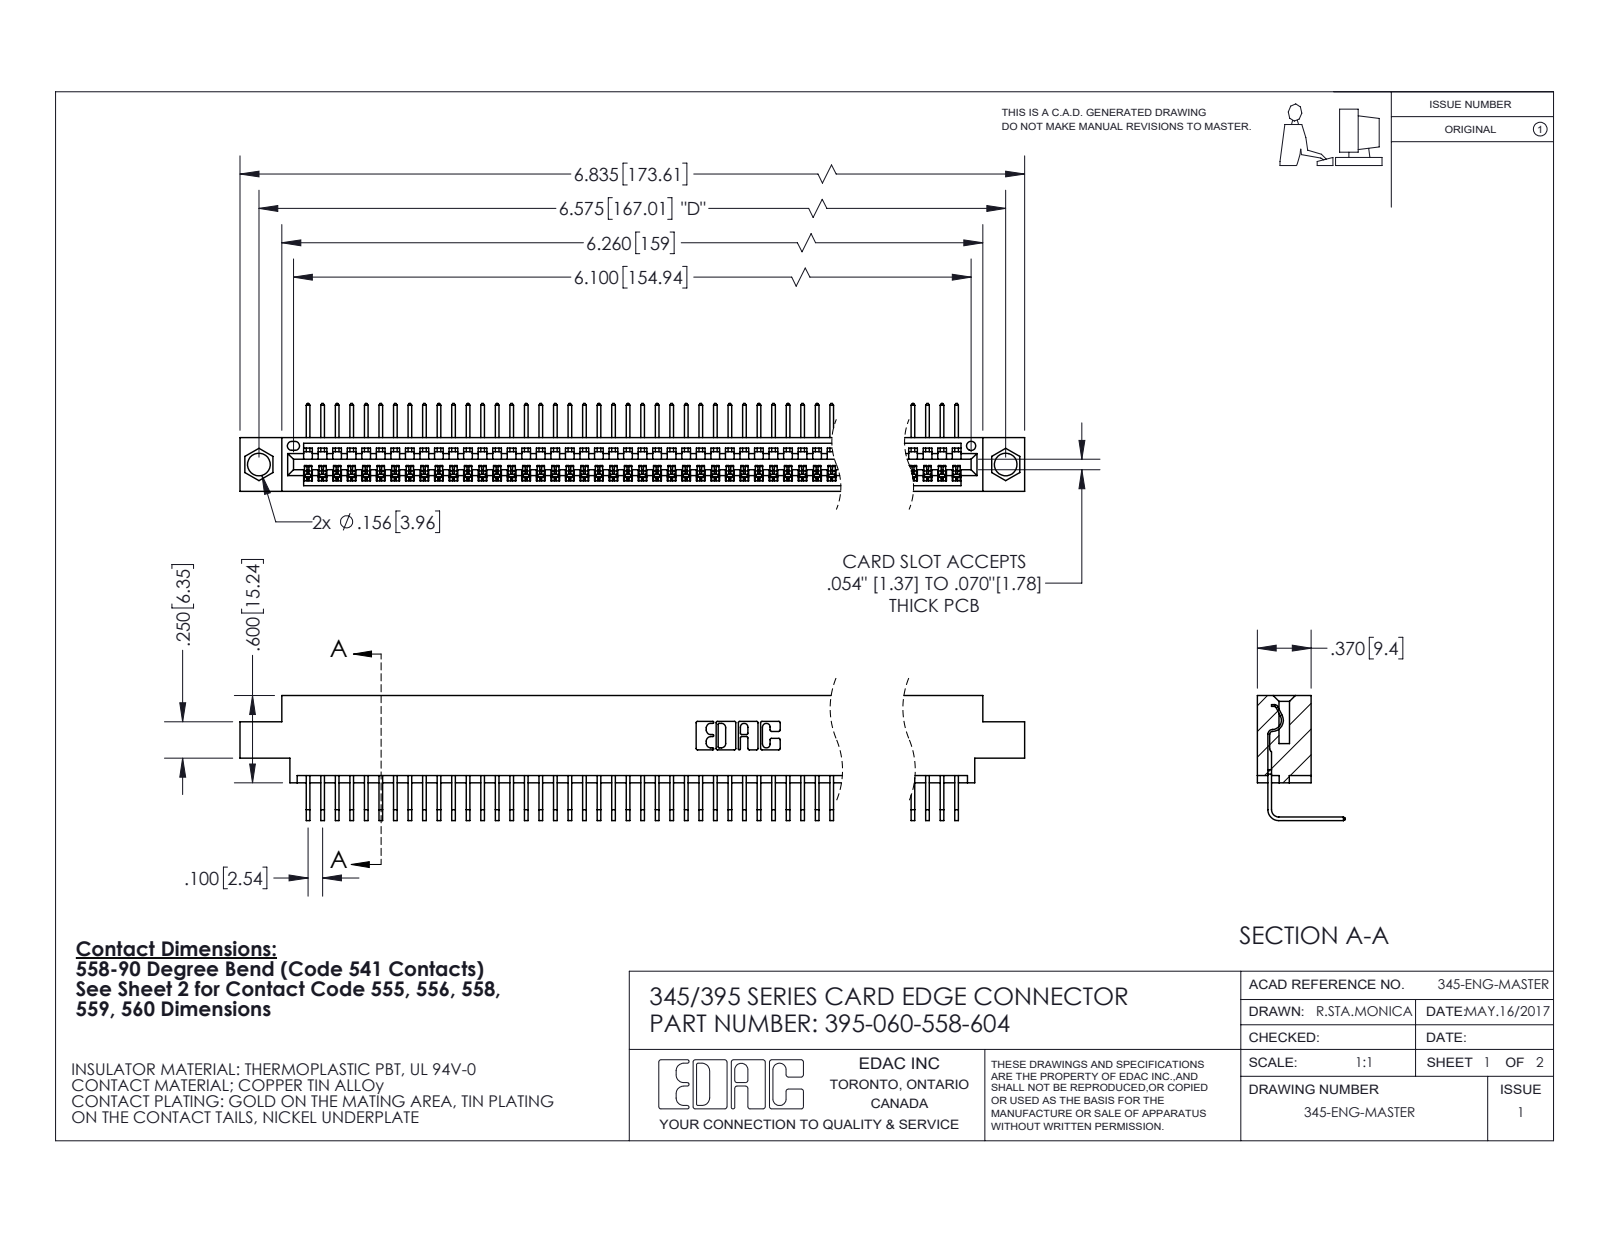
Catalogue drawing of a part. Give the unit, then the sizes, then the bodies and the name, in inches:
Units: inches
Overall size (bounding box): 6.835 × 0.859 × 0.605
Round holes (diameter × count): ⌀0.156 ×2, ⌀0.064 ×1
Partial cylindrical surfaces — rounded edges, fillets, slot ends (radius × count): R0.006 ×120, R0.01 ×22, R0.007 ×6, R0.031 ×6, R0.026 ×3, R0.031 ×2, R0.04 ×2, R0.014 ×1
Main face-to-face distances: 0.072, 0.298, 0.37, 0.2, 0.098, 0.272, 0.025, 0.225, 0.175, 0.149
Hole centre spacings: 0.27, 6.339, 6.575
Volume: 1.014 in³ · Surface area: 36.38 in²
Bodies: 61 solids, 3744 faces (2618 planar, 1126 cylindrical, 0 other)
Part name (STEP PRODUCT): 395-060-558-604; 345 Part_0.170 Offset - 0.156 Dia-TI; 345-292-001_558 Tail - 2
STEP written by: SolidWorks 2020 (CONFIG_CONTROL_DESIGN)
